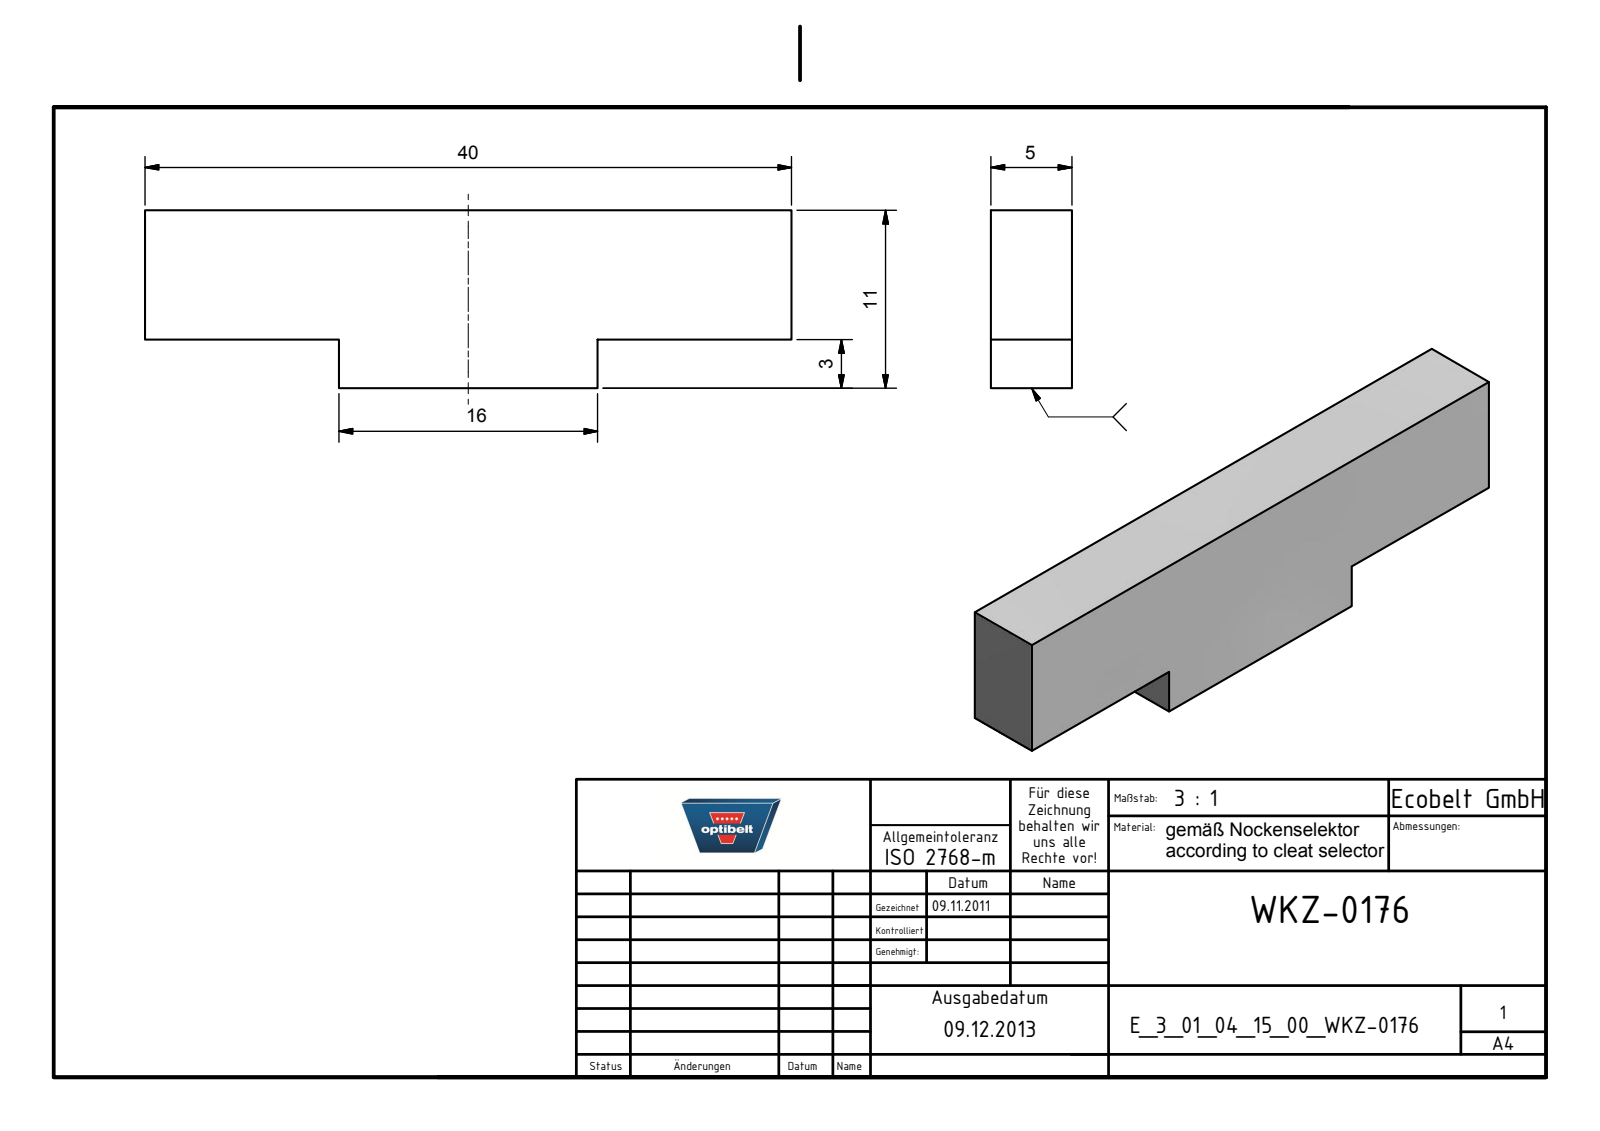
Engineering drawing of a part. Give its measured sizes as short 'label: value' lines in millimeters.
name: E_3_01_04_15_00_WKZ-0176
written by: Autodesk Inventor 2025 (AUTOMOTIVE_DESIGN)
unit: mm
bodies: 1 solid, 10 faces (10 planar, 0 cylindrical, 0 other)
size: 40 × 11 × 5
volume: 1 840 mm³; area: 1 246 mm²
face distances: 5, 8, 3, 11, 40, 12, 28, 16
